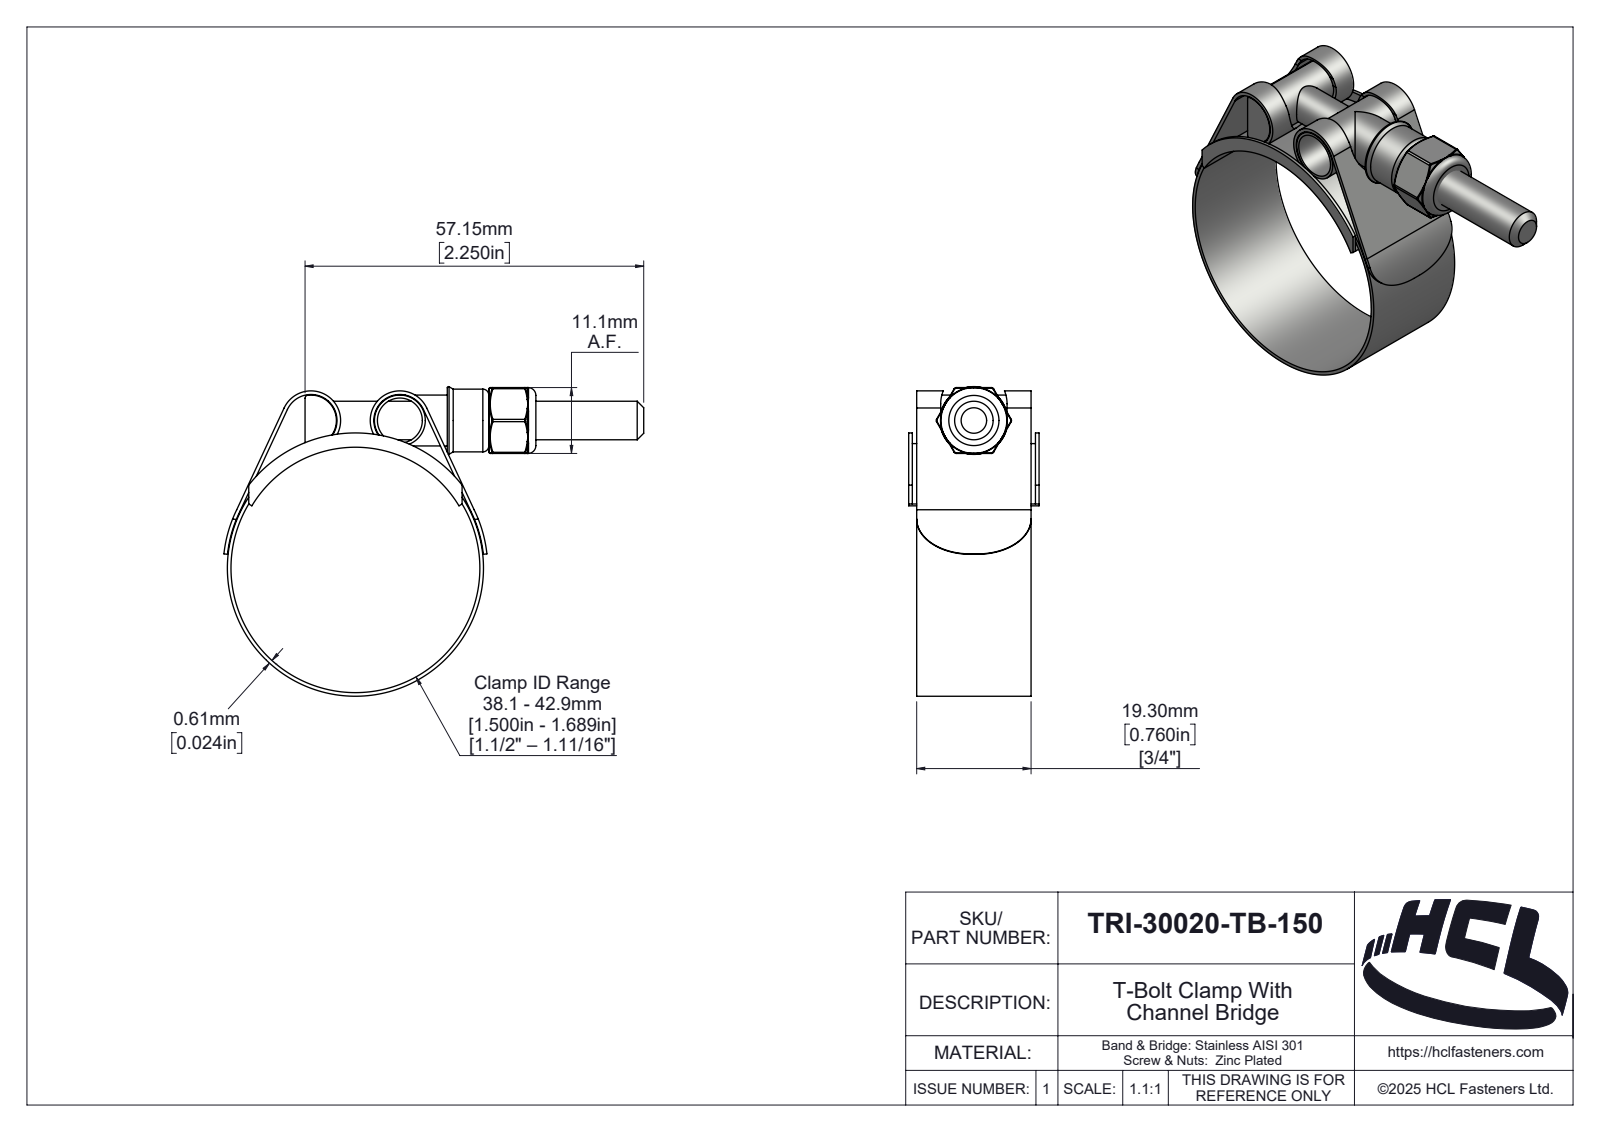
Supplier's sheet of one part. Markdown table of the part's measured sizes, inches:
| quantity | value |
| --- | --- |
| part name | TRI-30020-TB-150 |
| STEP written by | SolidWorks 2025 (AUTOMOTIVE_DESIGN) |
| units | inches |
| bodies | 6 solids, 338 faces (48 planar, 126 cylindrical, 164 other) |
| overall size | 2.789 × 2.056 × 0.866 |
| volume | 0.402 in³ |
| surface area | 21.33 in² |
| round holes (diameter × count) | 0.213 × 1, 0.25 × 1, 0.256 × 1, 0.298 × 1, 1.654 × 1 |
| round bosses / shafts (diameter × count) | 0.338 × 2, 1.702 × 1, 0.417 × 1 |
| partial cylindrical surfaces (radius × count) | 0.015 × 6, 0.02 × 2, 0.173 × 2, 0.197 × 2, 0.22 × 2, 0.023 × 1, 0.095 × 1, 0.119 × 1 |
| main face-to-face distances | 0.024, 0.029, 0.053, 0.813, 0.76, 0.842, 0.789, 0.437, 0.866, 1.22 |
| hole center spacings | 1.024 |
